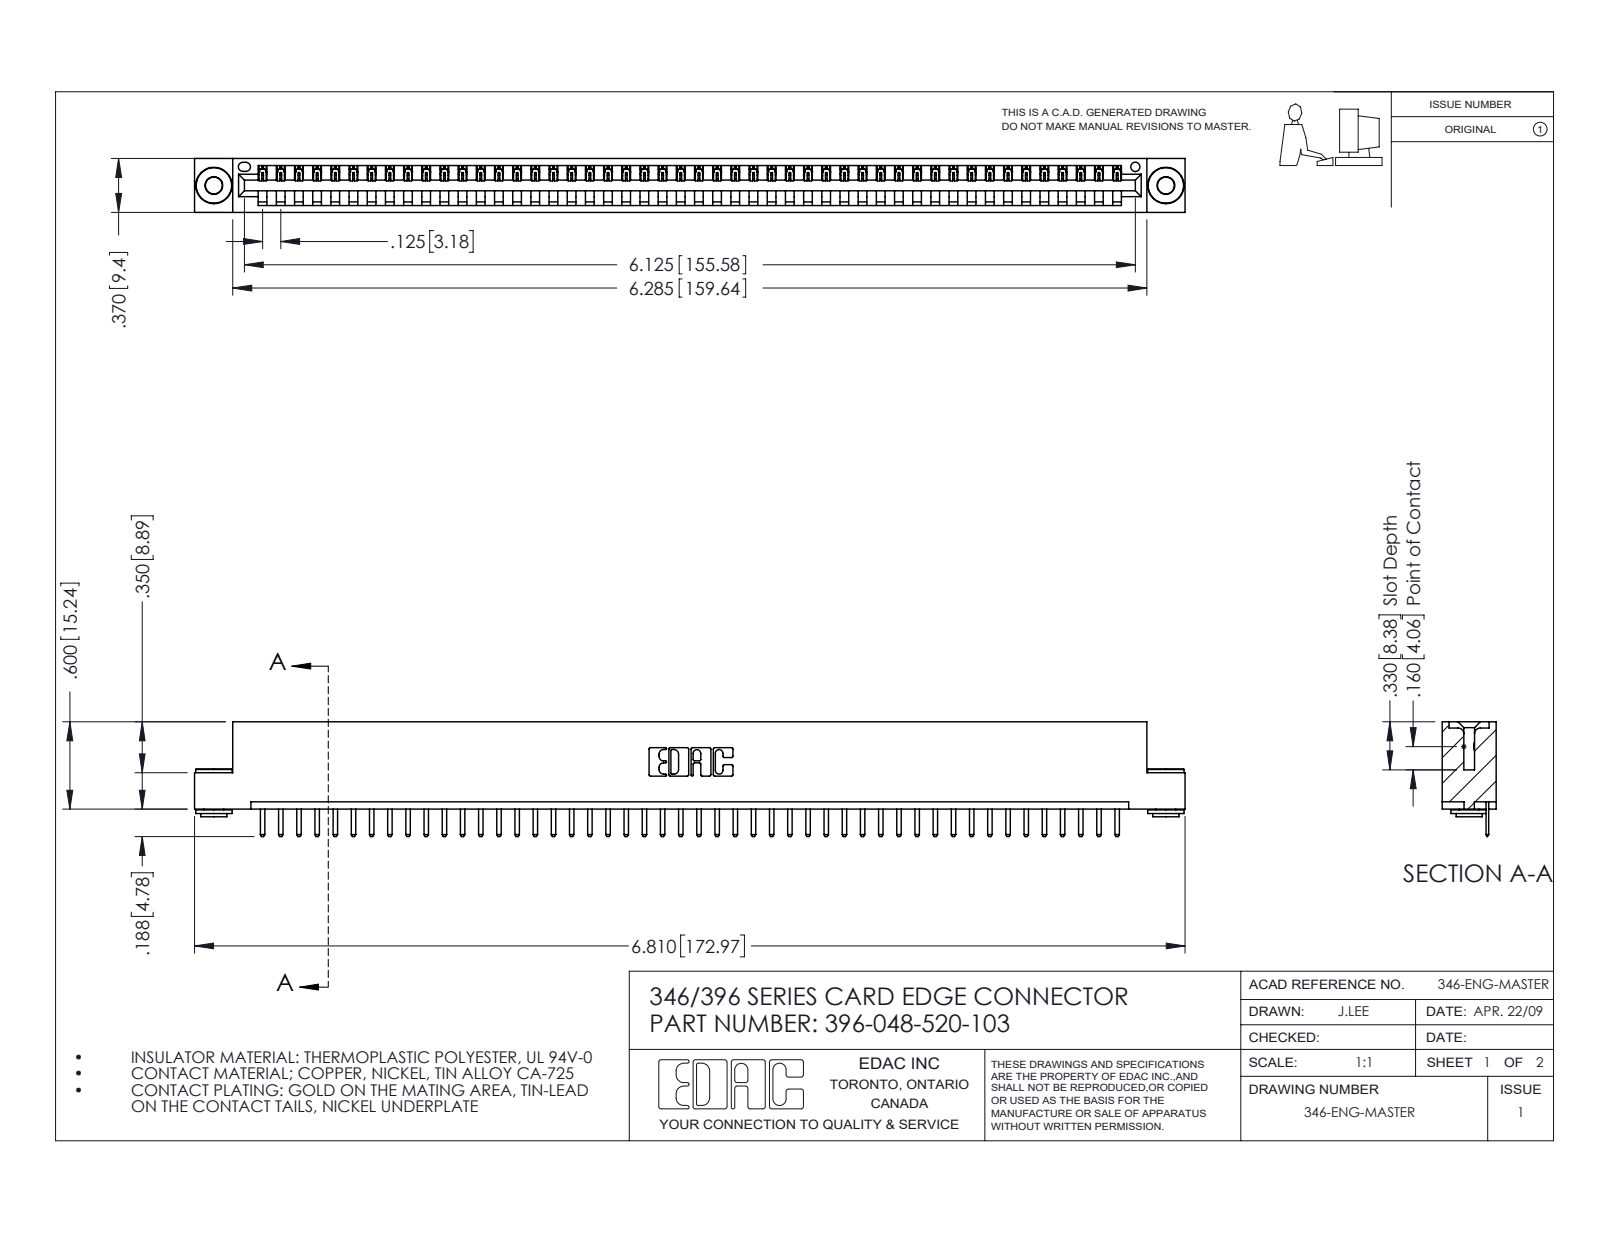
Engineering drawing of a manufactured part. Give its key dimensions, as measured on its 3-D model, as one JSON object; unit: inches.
{"part_name": "345-292-001_345-293-120; 396-048-520-103; 345-250-002_345-250-002-102; 346 Part_Flush Mounting Lugs - 0.156 Dia-TH", "step_written_by": "SolidWorks 2016 (CONFIG_CONTROL_DESIGN)", "units": "inches", "bodies": {"solids": 51, "faces": 3136, "planar": 2102, "cylindrical": 1026, "other": 8}, "overall_size": [6.81, 0.788, 0.37], "volume_in3": 1.006, "surface_area_in2": 31.65, "round_holes": [[0.116, 2], [0.156, 2], [0.064, 1]], "round_bosses_or_shafts": [[0.25, 2], [0.18, 2], [0.136, 2]], "partial_cylinders_radius": [[0.01, 98], [0.006, 96], [0.01, 22], [0.007, 6], [0.031, 6], [0.026, 3], [0.031, 2], [0.04, 2]], "face_to_face_distances": [0.048, 0.322, 0.37, 0.25, 0.148, 0.222, 0.1, 0.174, 0.025, 0.072], "hole_center_spacings": [0.246, 6.336, 6.545]}
